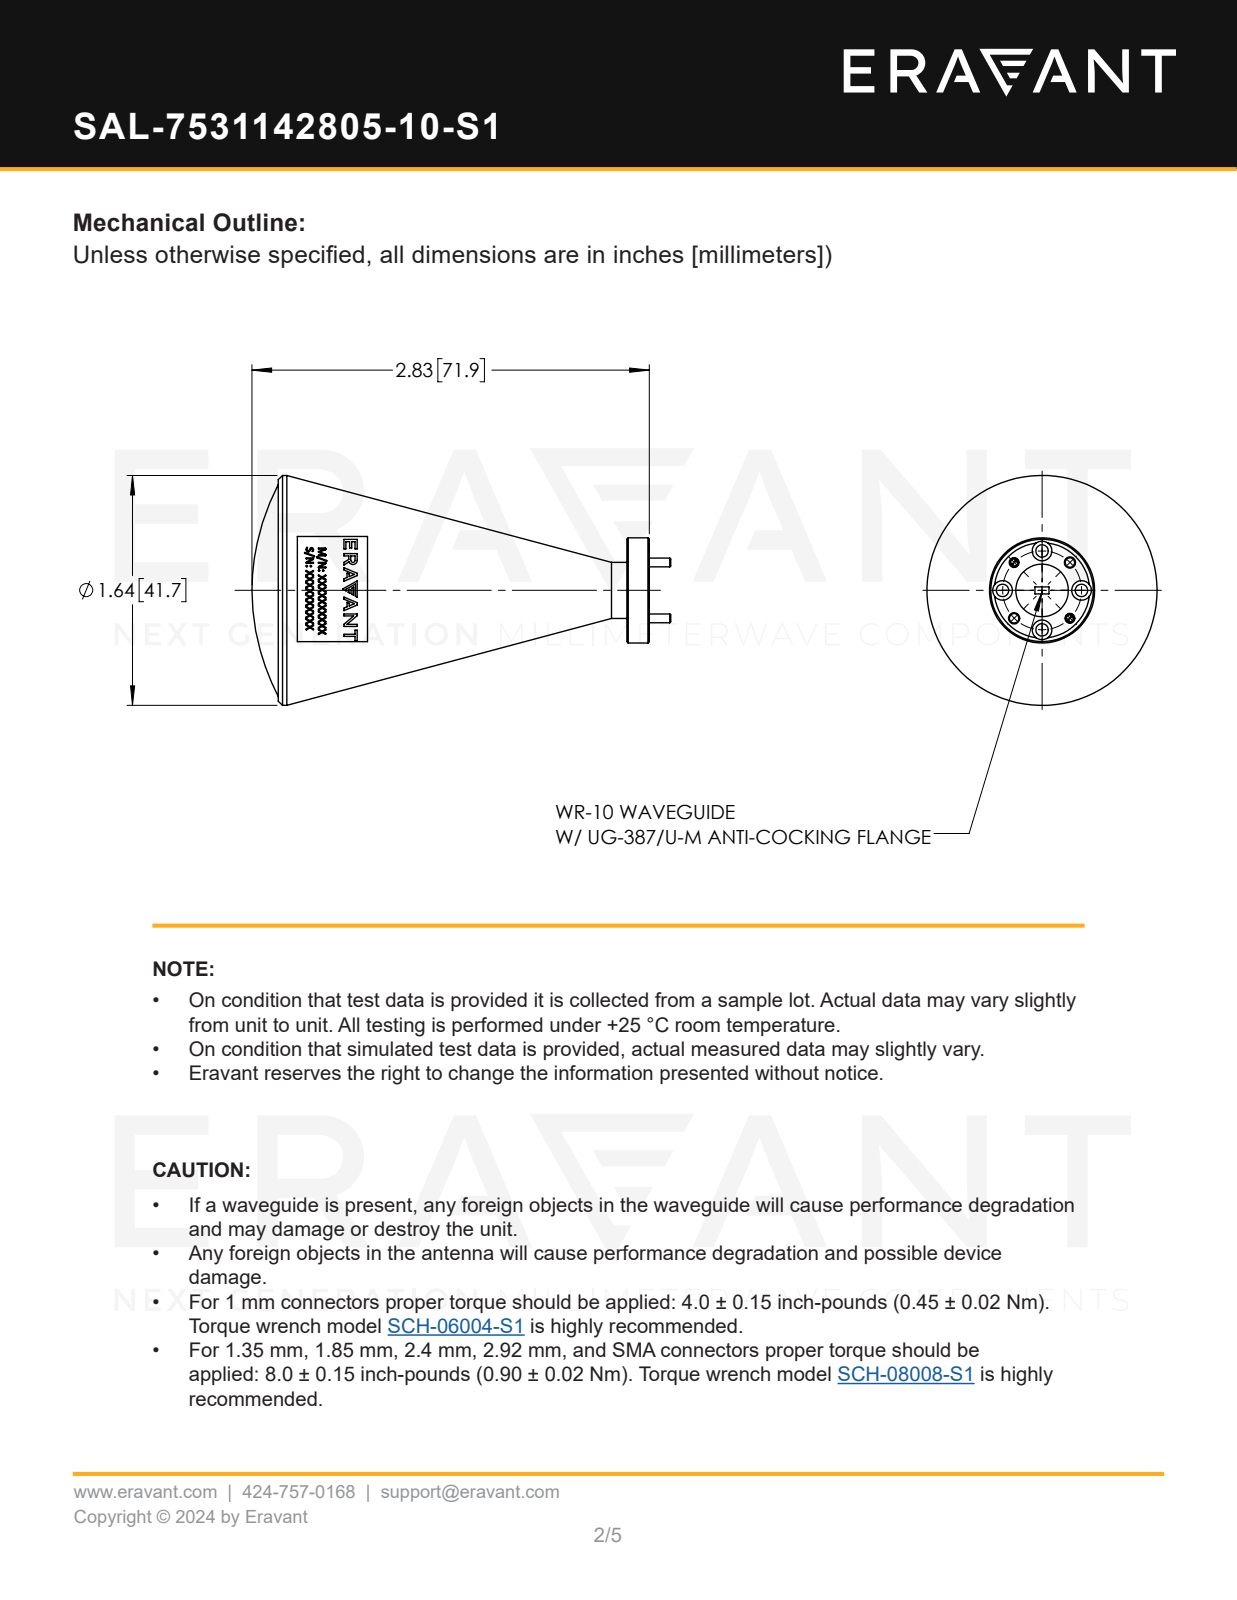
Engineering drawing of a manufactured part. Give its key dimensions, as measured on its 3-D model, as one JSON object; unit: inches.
{"part_name": "SAL-7531142805-10-S1", "step_written_by": "SolidWorks 2021 (CONFIG_CONTROL_DESIGN)", "units": "inches", "bodies": {"solids": 4, "faces": 85, "planar": 15, "cylindrical": 40, "other": 30}, "overall_size": [2.984, 1.64, 1.64], "volume_in3": 2.563, "surface_area_in2": 15.64, "round_holes": [[0.089, 4], [0.14, 4], [0.06, 2], [0.067, 2], [1.544, 1]], "round_bosses_or_shafts": [[0.063, 2], [1.64, 1], [1.54, 1], [0.75, 1], [0.4, 1], [0.375, 1]], "face_to_face_distances": [0.04, 2.474, 2.434, 2.604, 2.564, 0.13, 2.594, 0.05, 2.634, 0.16], "hole_center_spacings": [0.215, 0.398, 0.281, 0.519, 0.52, 0.281, 0.562, 0.563]}
